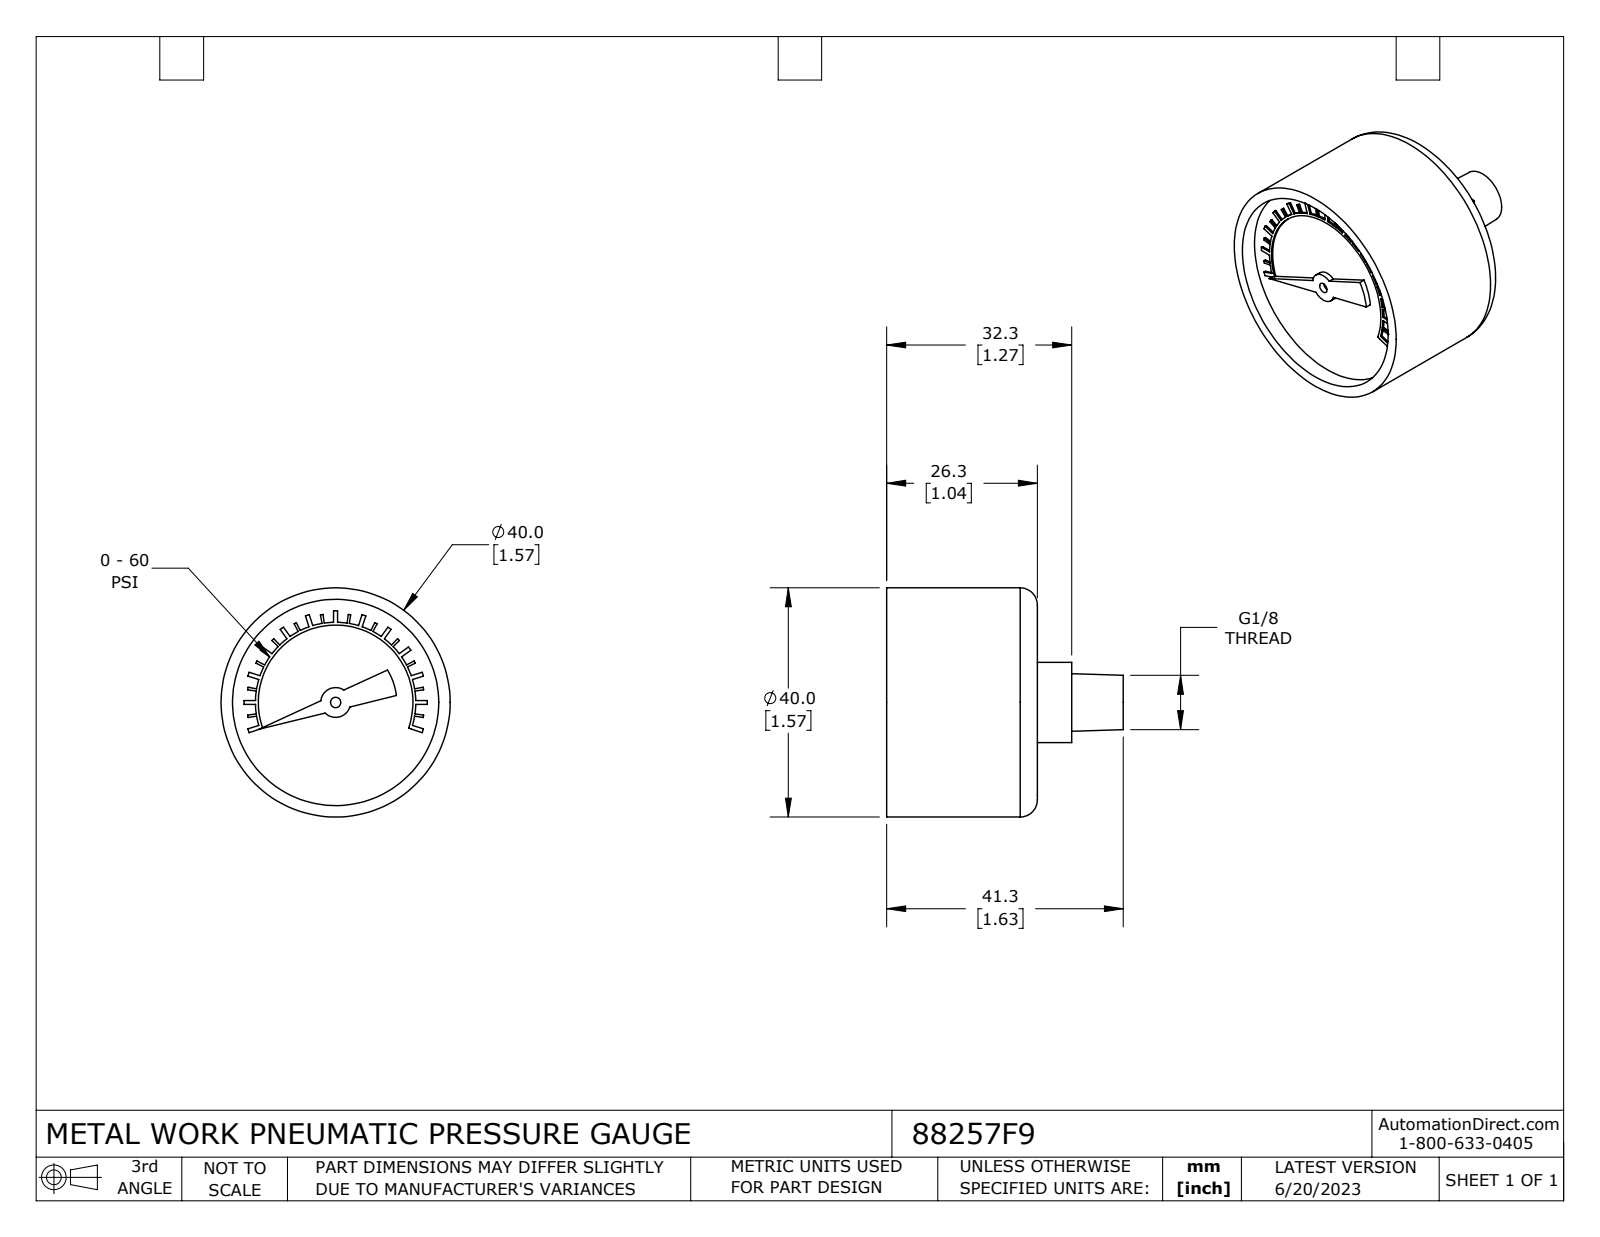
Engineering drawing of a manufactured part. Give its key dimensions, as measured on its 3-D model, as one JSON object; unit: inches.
{"part_name": "88257F9", "step_written_by": "SolidWorks 2021 (CONFIG_CONTROL_DESIGN)", "units": "inches", "bodies": {"solids": 1, "faces": 133, "planar": 93, "cylindrical": 36, "other": 4}, "overall_size": [1.626, 1.575, 1.575], "volume_in3": 1.934, "surface_area_in2": 10.41, "round_holes": [[0.071, 1], [1.417, 1]], "round_bosses_or_shafts": [[1.575, 1]], "partial_cylinders_radius": [[0.103, 1], [0.42, 1], [0.514, 1], [0.526, 1], [0.531, 1], [0.532, 1], [0.538, 1], [0.541, 1]], "face_to_face_distances": [0.917, 1.035, 0.118, 0.551, 0.236, 1.154, 1.272, 0.354, 0.591, 1.508]}
